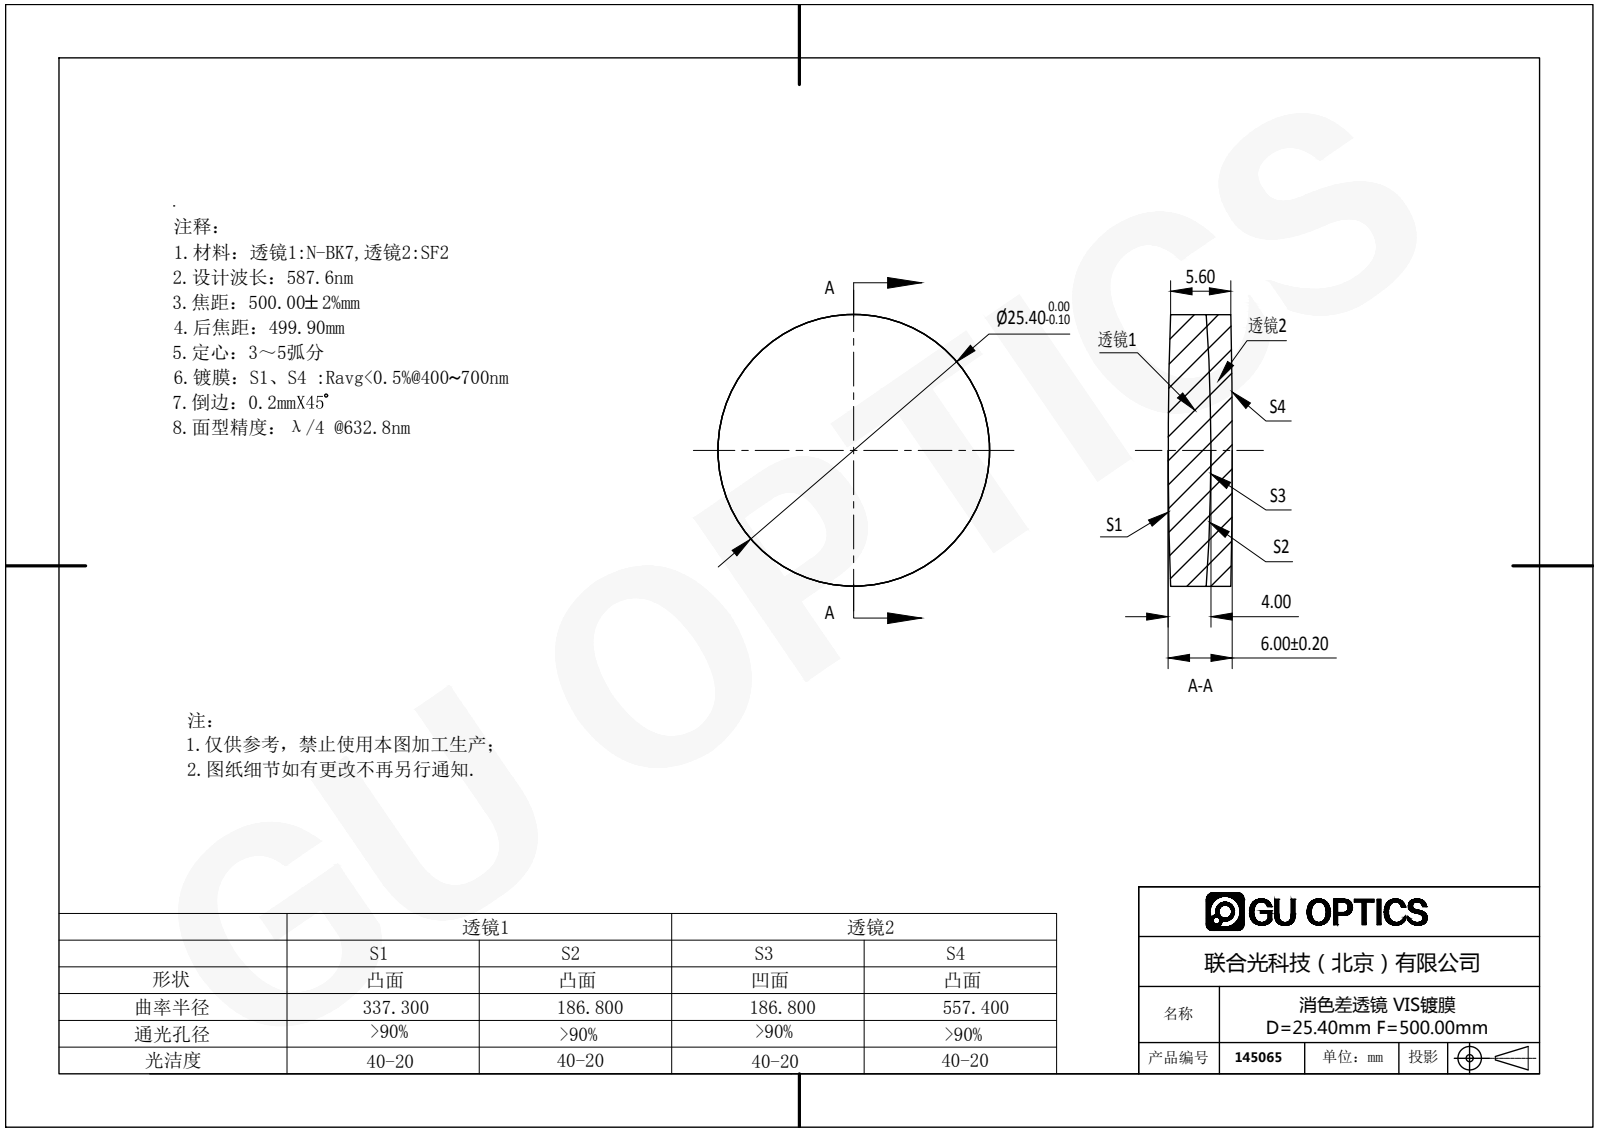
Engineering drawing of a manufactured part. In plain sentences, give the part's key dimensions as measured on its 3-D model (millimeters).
The part is named "145065". Its 3-D file was written by "SolidWorks 2016 (AUTOMOTIVE_DESIGN)". It is 2 solids with 12 faces: 0 planar, 4 cylindrical and 8 other. Overall it measures 25.4 by 25.4 by 6 millimeters. Its volume is 2 943 cubic millimeters and its surface area 2 476 square millimeters. Round bosses or shafts: 1 of diameter 25.4.
